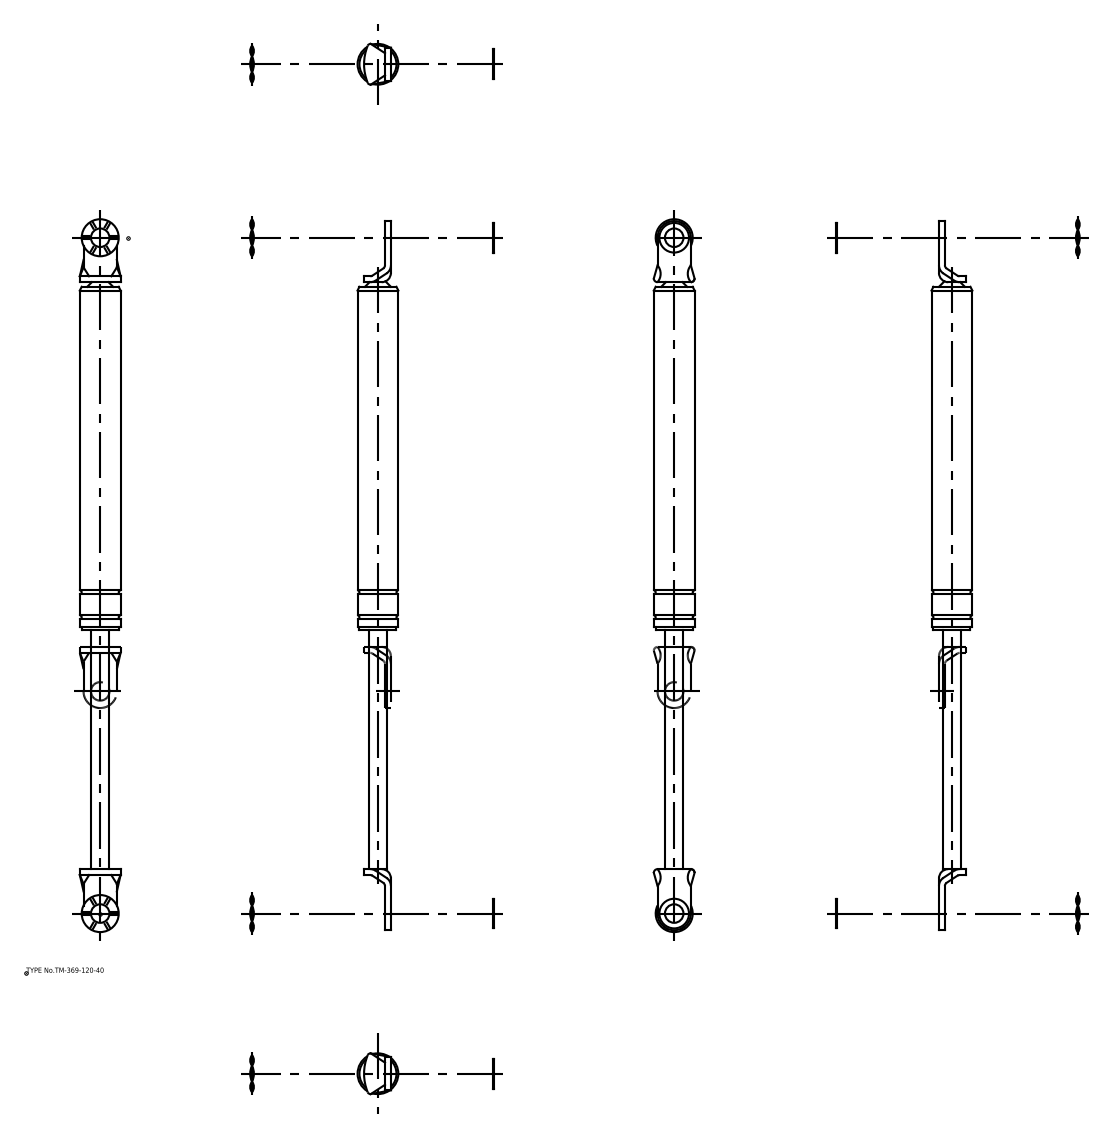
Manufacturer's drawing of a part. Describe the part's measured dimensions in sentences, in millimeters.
The part is named "ウェーブワッシャー; ワッシャー; 本体; 本体_div". Its 3-D file was written by "spGate 16.7.1 (AUTOMOTIVE_DESIGN)". It is 6 solids with 95 faces: 43 planar, 44 cylindrical and 8 other. Overall it measures 385 by 22.5 by 22.5 millimeters. Its volume is 86 337 cubic millimeters and its surface area 23 329 square millimeters. Round holes: 2 of diameter 10. Round bosses or shafts: 3 of diameter 20, 2 of diameter 16, 1 of diameter 22.5, 1 of diameter 22, 1 of diameter 10. Partial cylindrical surfaces (rounded edges, fillets, slot ends): 2 of radius 4.4, 2 of radius 5, 2 of radius 9, 1 of radius 26.32. The main face-to-face distances are 3.2, 2, 5.2, 5.7, 320.2, 3.7, 0.5, 191.2, 132.2, 323.4. The hole center spacings are 365.
